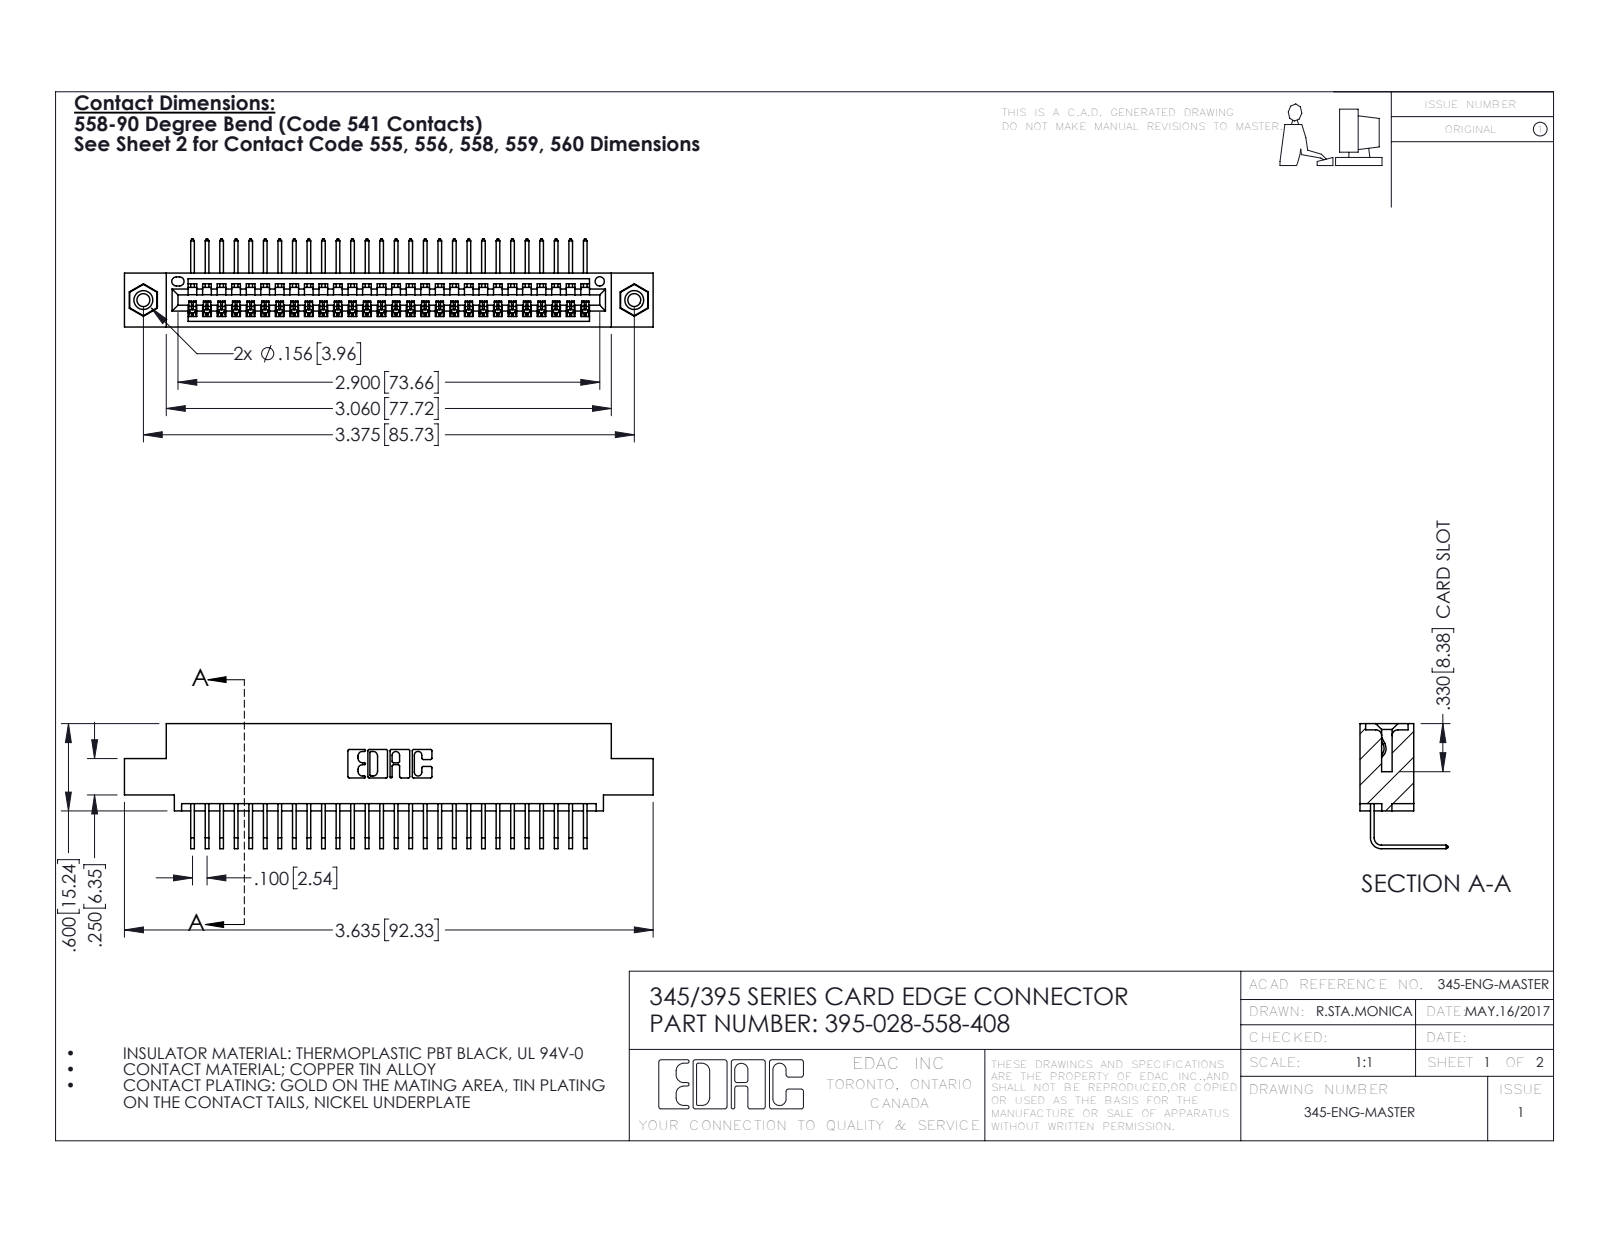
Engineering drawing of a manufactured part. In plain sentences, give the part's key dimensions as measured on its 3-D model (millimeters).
The part is named "345 Part_0.110 Offset - 0.156 Dia-TI; 345-292-001_558 Tail - 2; 395-028-558-408; 345-250-001_345-250-003-102". Its 3-D file was written by "SolidWorks 2016 (CONFIG_CONTROL_DESIGN)". It is 31 solids with 1870 faces: 1292 planar, 562 cylindrical and 16 other. Overall it measures 92.3 by 21.8 by 15.4 millimeters. Its volume is 8 670 cubic millimeters and its surface area 11 980 square millimeters. Round holes: 2 of diameter 2.3, 2 of diameter 3.2, 2 of diameter 4, 1 of diameter 1.6. Round bosses or shafts: 2 of diameter 3.9. Partial cylindrical surfaces (rounded edges, fillets, slot ends): 56 of radius 0.2, 22 of radius 0.3, 6 of radius 0.2, 6 of radius 0.8, 3 of radius 0.7, 2 of radius 0.8, 2 of radius 1, 1 of radius 0.4. The main face-to-face distances are 1.8, 7.6, 9.4, 5.1, 2.5, 6.9, 0.6, 5.7, 3.8, 1.8. The hole center spacings are 6.9, 79.8, 85.7.
